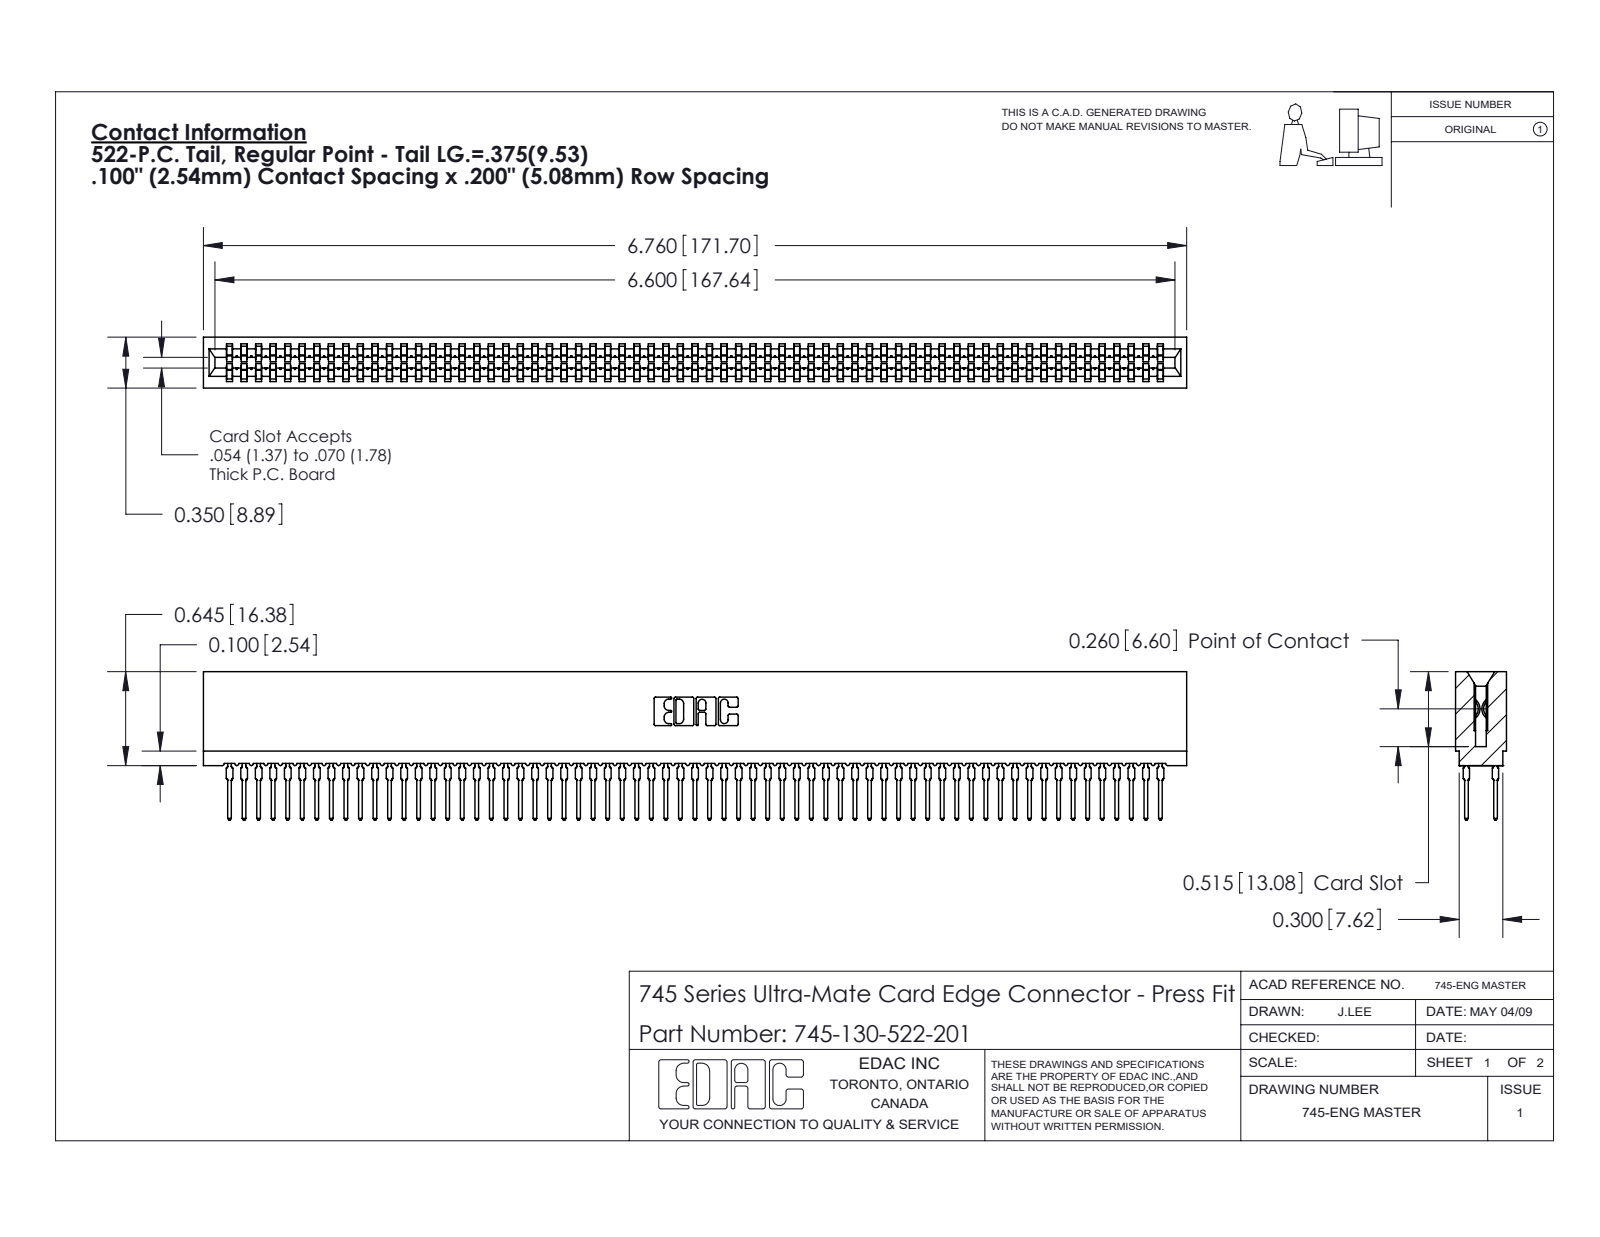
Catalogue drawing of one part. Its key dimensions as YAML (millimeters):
part_name: "745-292-001_522; 745 Part_Insulator Option - 01; 745-130-522-201"
step_written_by: "SolidWorks 2020 (CONFIG_CONTROL_DESIGN)"
units: millimeters
bodies: {solids: 131, faces: 11730, planar: 6035, cylindrical: 2315, other: 3380}
overall_size: [171.7, 25.9, 8.9]
volume: 15500
surface_area: 32410
partial_cylinders:
  - {radius: 0.5, count: 260}
  - {radius: 0.4, count: 130}
  - {radius: 0.3, count: 22}
  - {radius: 0.1, count: 8}
  - {radius: 0.3, count: 8}
  - {radius: 0.2, count: 6}
  - {radius: 0.8, count: 6}
  - {radius: 0.7, count: 3}
face_to_face_distances: [8.9, 1.6, 7.3, 1.1, 7.7, 0.5, 6.2, 3.5, 5.4, 2.4]
